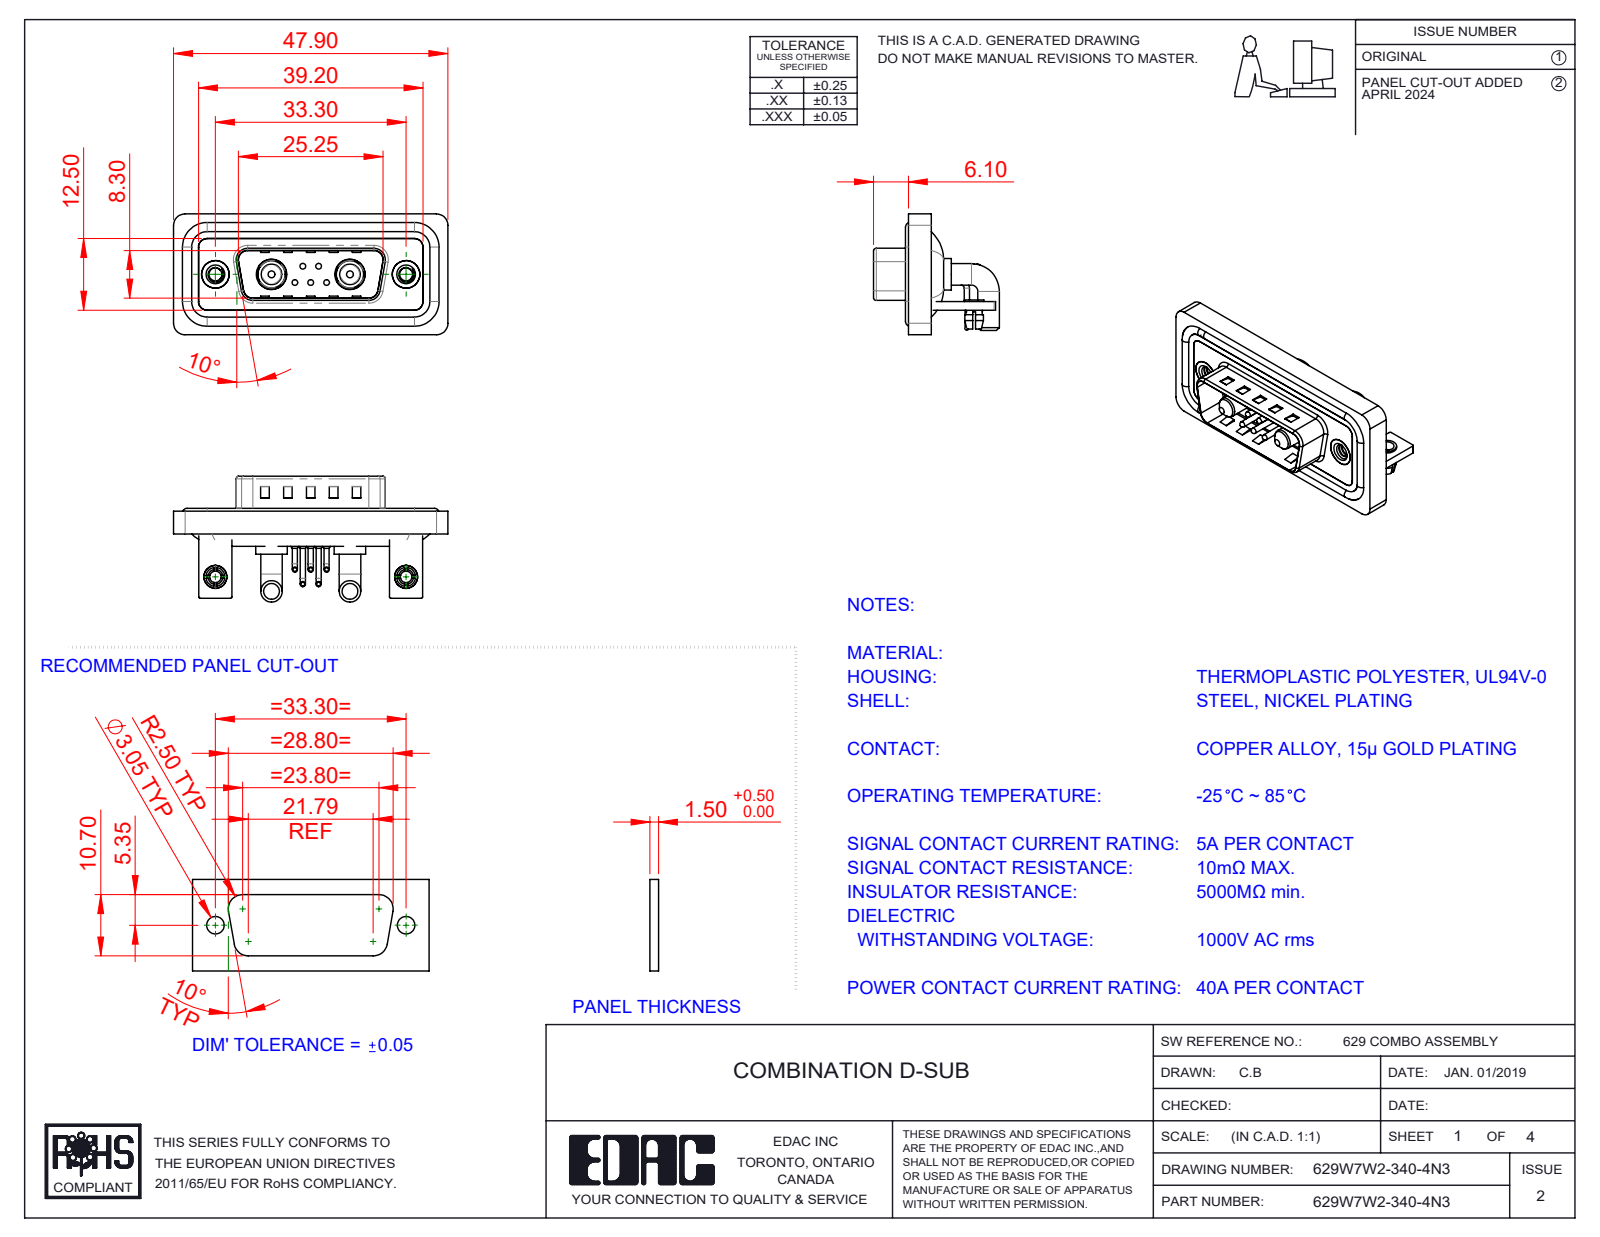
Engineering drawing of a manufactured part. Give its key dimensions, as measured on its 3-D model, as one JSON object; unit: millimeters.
{"part_name": "629Combo Shell Front_15 Contacts; 629Combo Threaded Rivet_3; 629Combo Contact Row 1; 629Combo Board Lock (+7 more)", "step_written_by": "SolidWorks 2023 (CONFIG_CONTROL_DESIGN)", "units": "millimeters", "bodies": {"solids": 20, "faces": 1215, "planar": 585, "cylindrical": 456, "other": 174}, "overall_size": [47.9, 21.98, 21.1], "volume_mm3": 6140, "surface_area_mm2": 10026, "round_holes": [[2, 7], [0.75, 5], [1.6, 5], [2.26, 2], [2.5, 2], [3.2, 2], [4, 2], [4.8, 2], [4.85, 2], [5, 2], [5.3, 2]], "round_bosses_or_shafts": [[0.9, 10], [1.5, 5], [1, 5], [0.65, 5], [3.75, 4], [1.6, 4], [5.5, 2], [5.2, 2]], "partial_cylinders_radius": [[2, 21], [1.5, 18], [0.25, 16], [0.5, 9], [1.6, 8], [1.01, 5], [0.6, 4], [0.65, 4]], "face_to_face_distances": [0.4, 0.8, 1.5, 2.9, 2.1, 1.1, 1.6, 1.2, 3.7, 4.5], "hole_center_spacings": [3.16, 2.77, 9.8, 23.5, 33.3, 4.31, 4.33, 5.03]}
